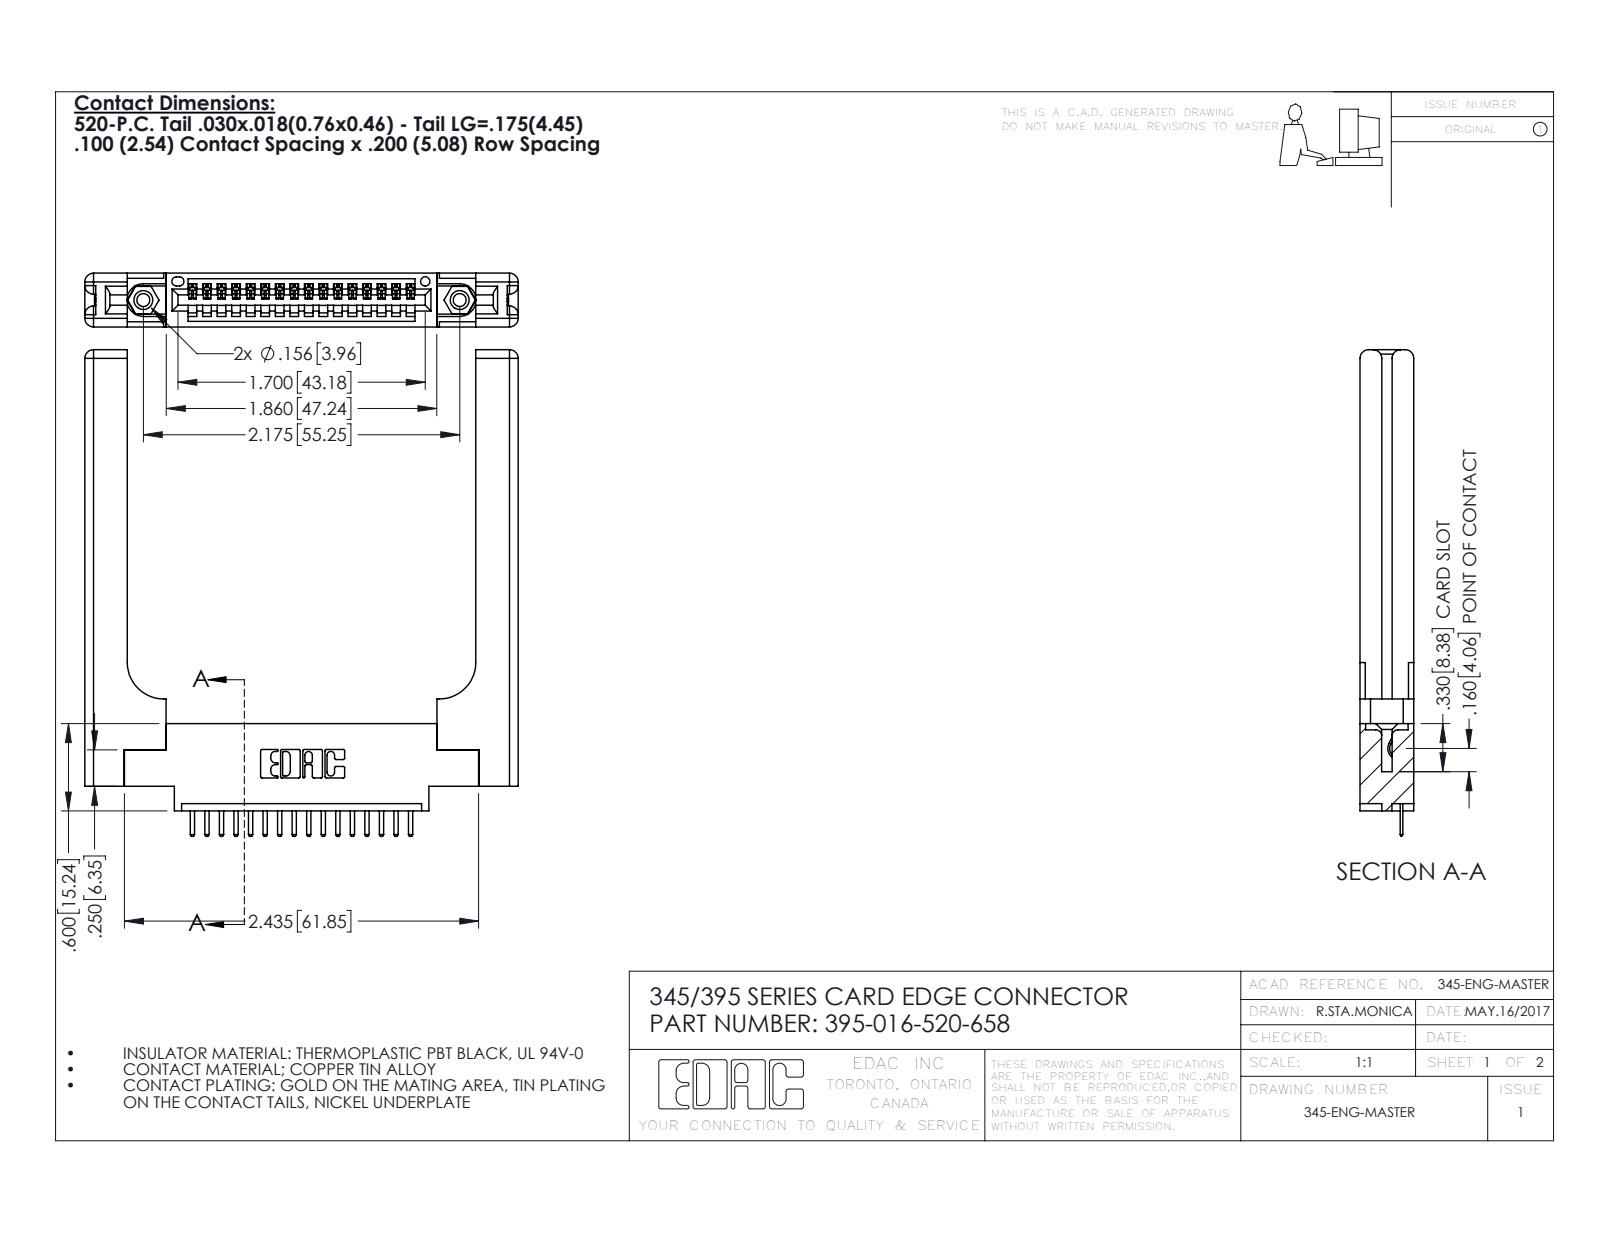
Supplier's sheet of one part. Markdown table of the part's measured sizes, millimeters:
| quantity | value |
| --- | --- |
| part name | 345 Part_0.170 Offset - 0.156 Dia-TH; 345-220-058_345-220-058; 395-016-520-658; 345-250-001_345-250-001-102 (+1 more) |
| STEP written by | SolidWorks 2016 (CONFIG_CONTROL_DESIGN) |
| units | millimeters |
| bodies | 21 solids, 1378 faces (904 planar, 414 cylindrical, 60 other) |
| overall size | 85 × 75.7 × 9.4 |
| volume | 15 300 mm³ |
| surface area | 13 990 mm² |
| round holes (diameter × count) | 2.3 × 2, 3.2 × 2, 4 × 2, 1.6 × 1 |
| round bosses / shafts (diameter × count) | 3.9 × 2 |
| partial cylindrical surfaces (radius × count) | 0.3 × 34, 0.2 × 32, 0.3 × 22, 1.5 × 16, 0.2 × 6, 0.8 × 6, 0.7 × 3, 0.8 × 2 |
| main face-to-face distances | 9.4, 1.8, 7.6, 3.8, 3.8, 2, 5.6, 3, 5.7, 60.9 |
| hole center spacings | 6.9, 49.3, 55.2 |
